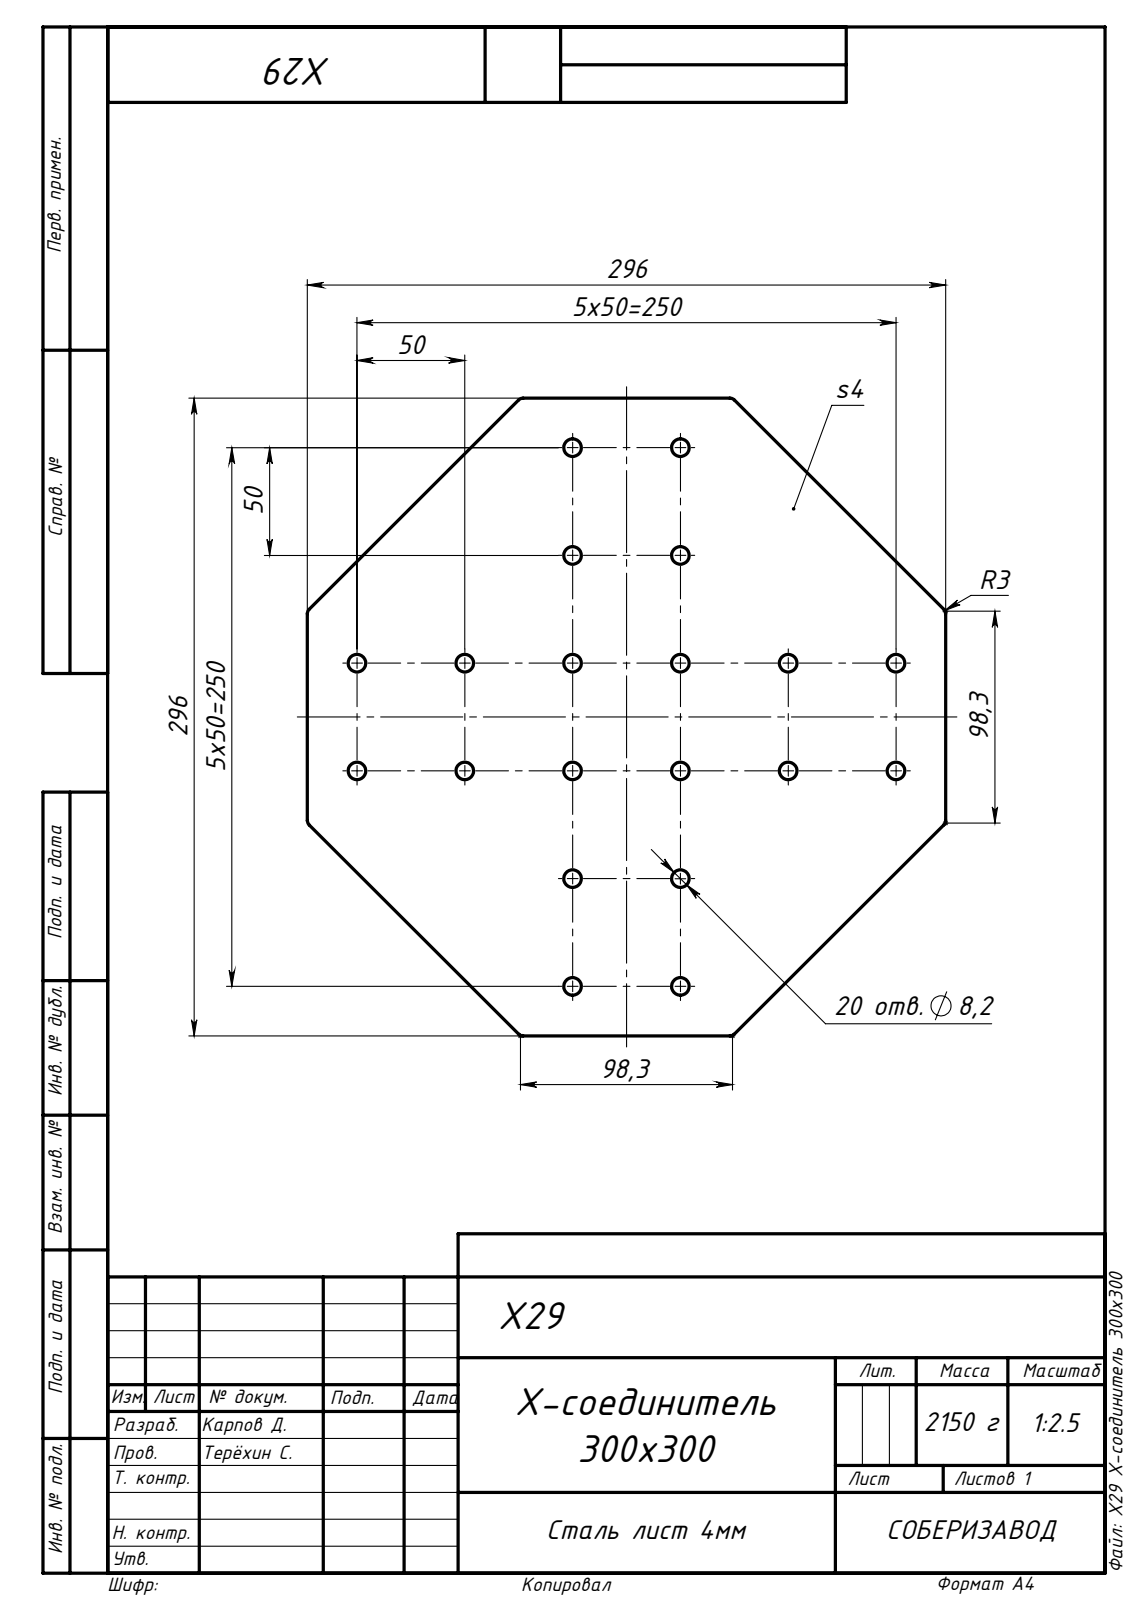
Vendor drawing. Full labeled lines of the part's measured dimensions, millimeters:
Part name (STEP PRODUCT): X29 Х-соединитель 300х300
STEP written by: SolidWorks 2019 (AUTOMOTIVE_DESIGN)
Units: millimetres
Bodies: 1 solid, 58 faces (10 planar, 48 cylindrical, 0 other)
Overall size (bounding box): 296 × 296 × 4
Volume: 268 097 mm³ · Surface area: 139 915 mm²
Round holes (diameter × count): ⌀8.2 ×20
Partial cylindrical surfaces — rounded edges, fillets, slot ends (radius × count): R3 ×8
Main face-to-face distances: 4, 278.8, 296
Hole centre spacings: 111.8, 50, 70.71, 158.11, 100, 141.42, 180.28, 150
